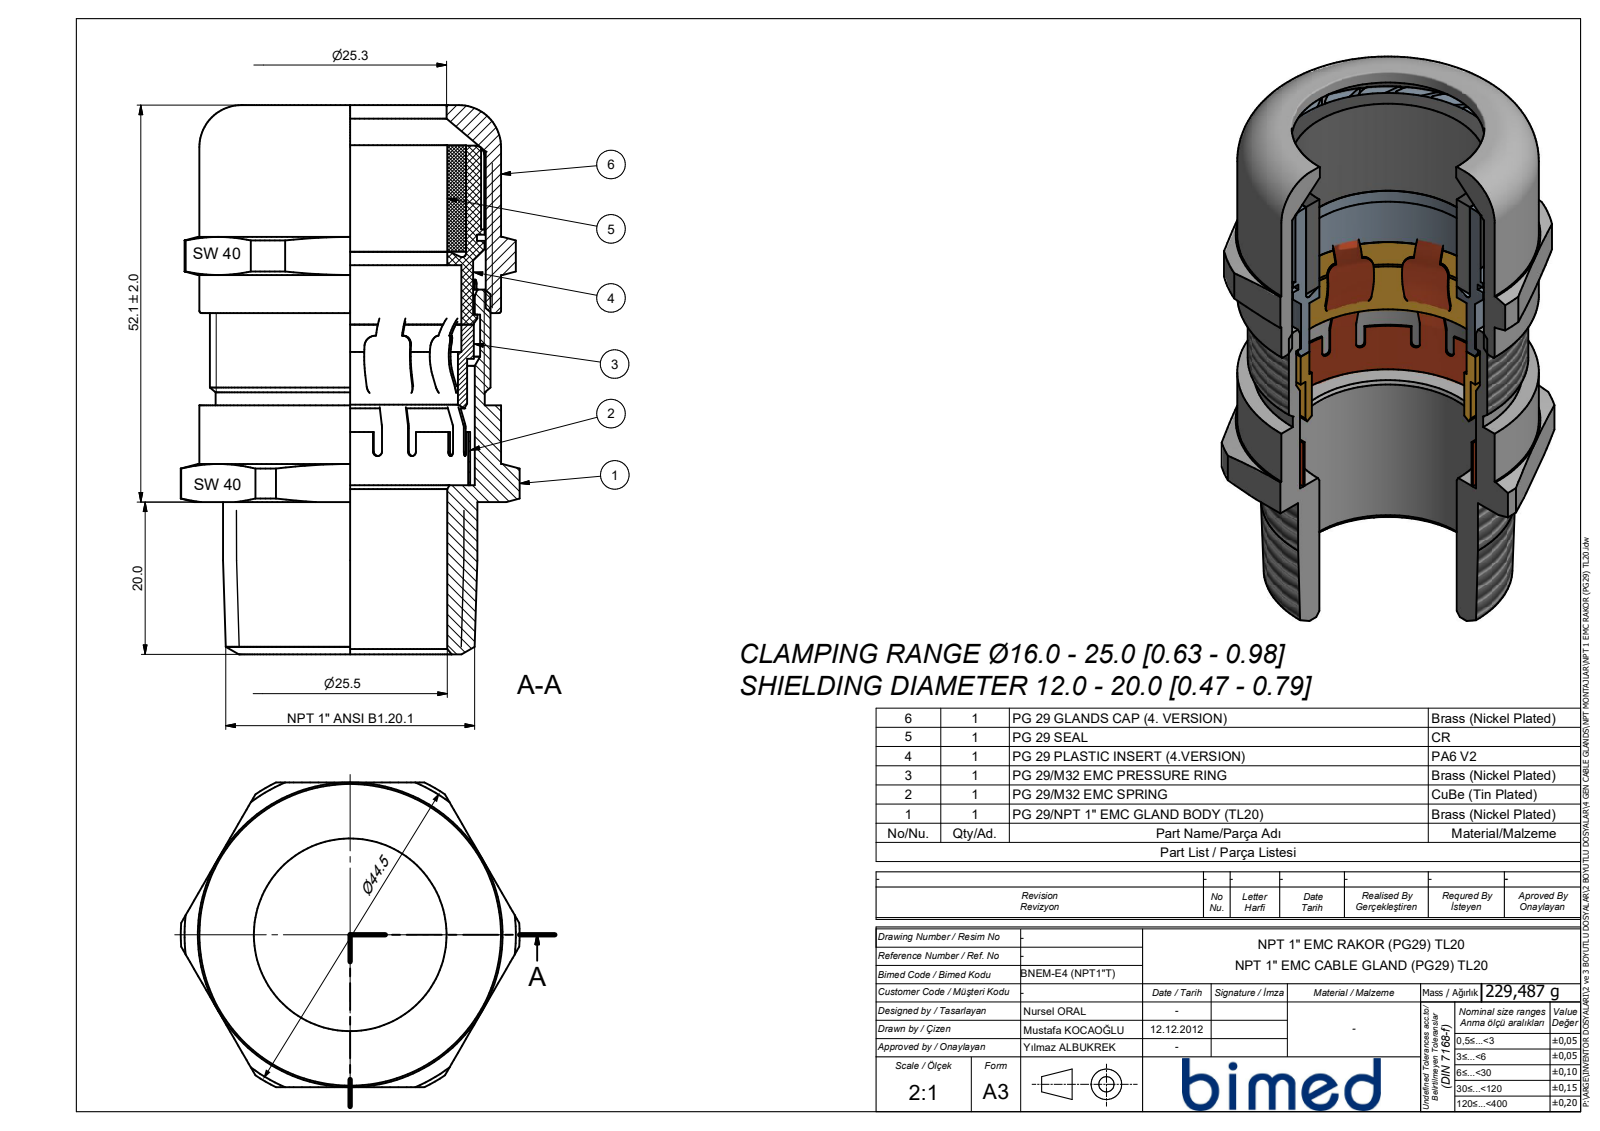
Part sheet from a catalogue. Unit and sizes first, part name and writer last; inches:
Units: inches
Overall size (bounding box): 2.839 × 1.752 × 1.575
Round bosses / shafts (diameter × count): ⌀1.559 ×1, ⌀1.451 ×1, ⌀1.391 ×1
Partial cylindrical surfaces — rounded edges, fillets, slot ends (radius × count): R0.856 ×1, R0.876 ×1
Main face-to-face distances: 2.839, 1.575, 0.787, 2.052, 1.287, 0.5, 1.552, 0.977, 1.764, 0.477
Volume: 4.866 in³ · Surface area: 17.81 in²
Bodies: 1 solid, 91 faces (21 planar, 26 cylindrical, 44 other)
Part name (STEP PRODUCT): BNEM-E4-1T-WCL
STEP written by: SolidWorks 2021 (CONFIG_CONTROL_DESIGN)
